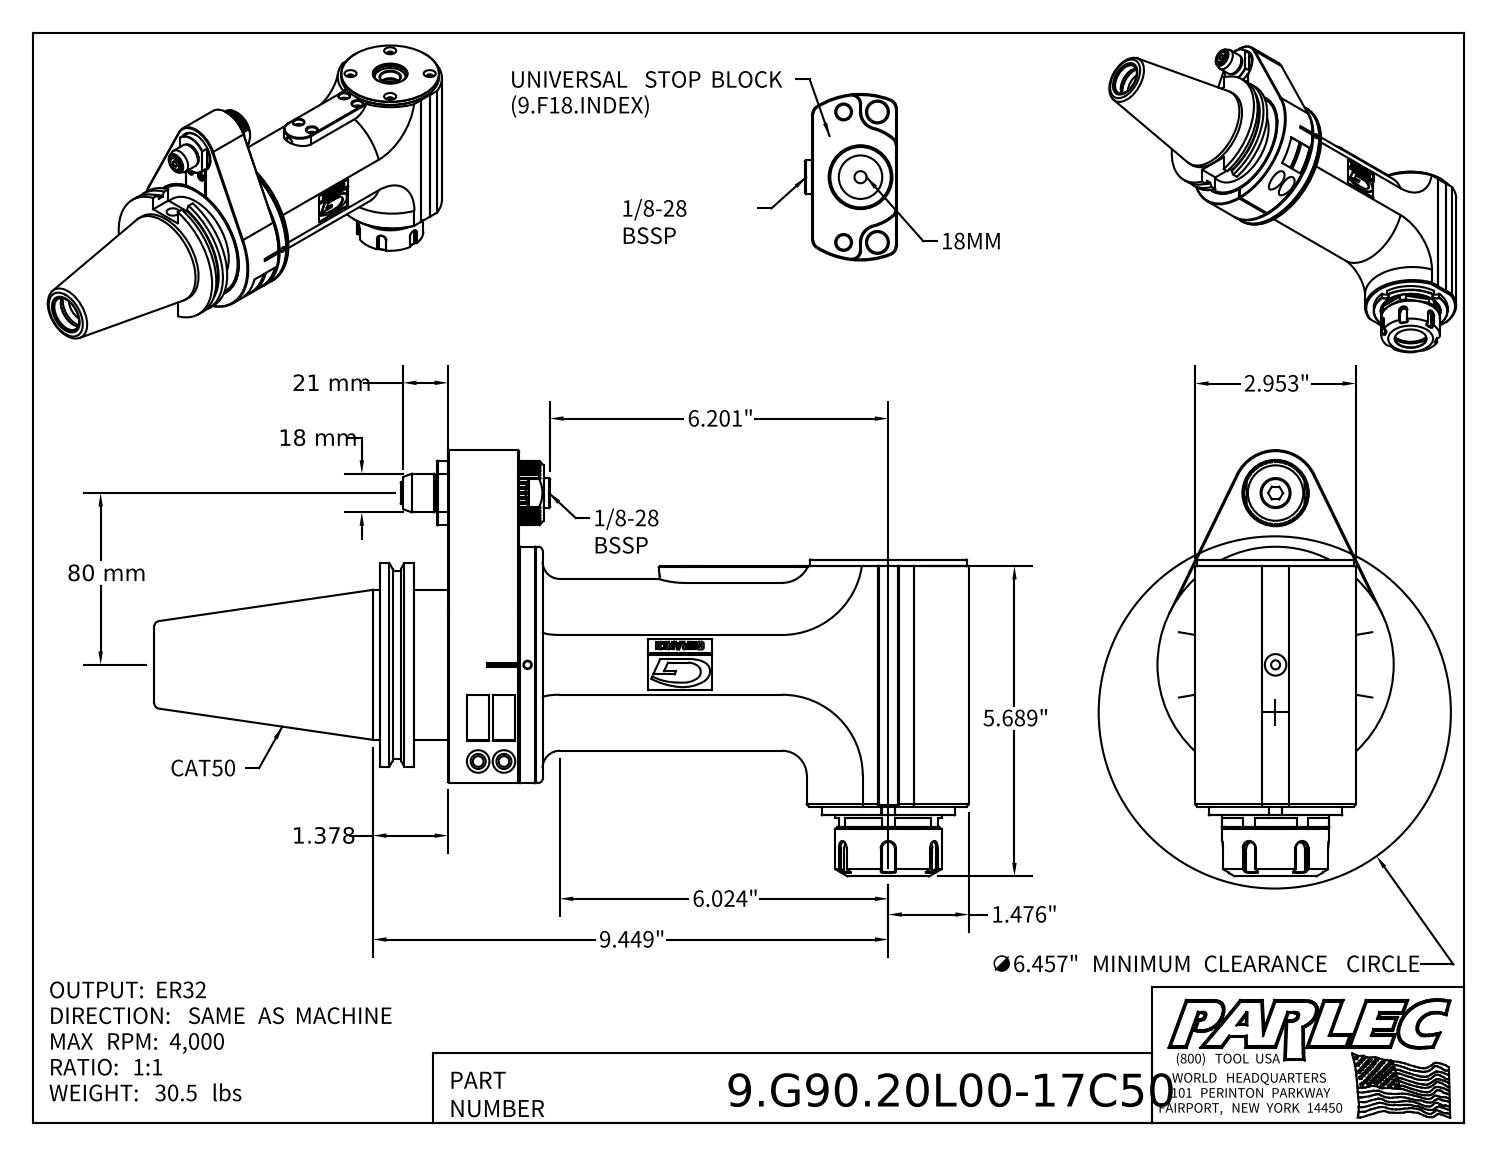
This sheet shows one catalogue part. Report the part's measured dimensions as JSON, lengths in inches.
{"part_name": "9.G90.20L00-17C50; 9_GA2_458_1 (Classic, Type 2, Cat50, 80mm); 9_G90_20L00", "step_written_by": "Autodesk Inventor 2022 (AUTOMOTIVE_DESIGN)", "units": "inches", "bodies": {"solids": 4, "faces": 936, "planar": 471, "cylindrical": 203, "other": 262}, "overall_size": [14.933, 7.815, 4.331], "volume_in3": 126.5, "surface_area_in2": 343.6, "round_holes": [[0.197, 13], [0.13, 9], [0.177, 8], [0.315, 4], [0.335, 4], [0.157, 2], [0.165, 2], [0.236, 2], [0.276, 2], [0.413, 2], [0.433, 2], [0.551, 1]], "round_bosses_or_shafts": [[0.394, 2], [4.331, 1], [4.016, 1], [3.875, 1], [3.593, 1], [3.524, 1], [3.15, 1], [2.874, 1]], "partial_cylinders_radius": [[0.118, 7], [0.085, 2], [0.315, 2], [0.469, 2], [0.472, 2], [1.575, 2], [0.079, 1], [0.098, 1]], "face_to_face_distances": [1.299, 0.315, 0.984, 0.626, 2.953, 0.118, 0.941, 1.925, 0.197, 2.551], "hole_center_spacings": [1.87, 3.239, 3.74, 0.968, 1.161, 1.643, 1.87, 2.645]}
